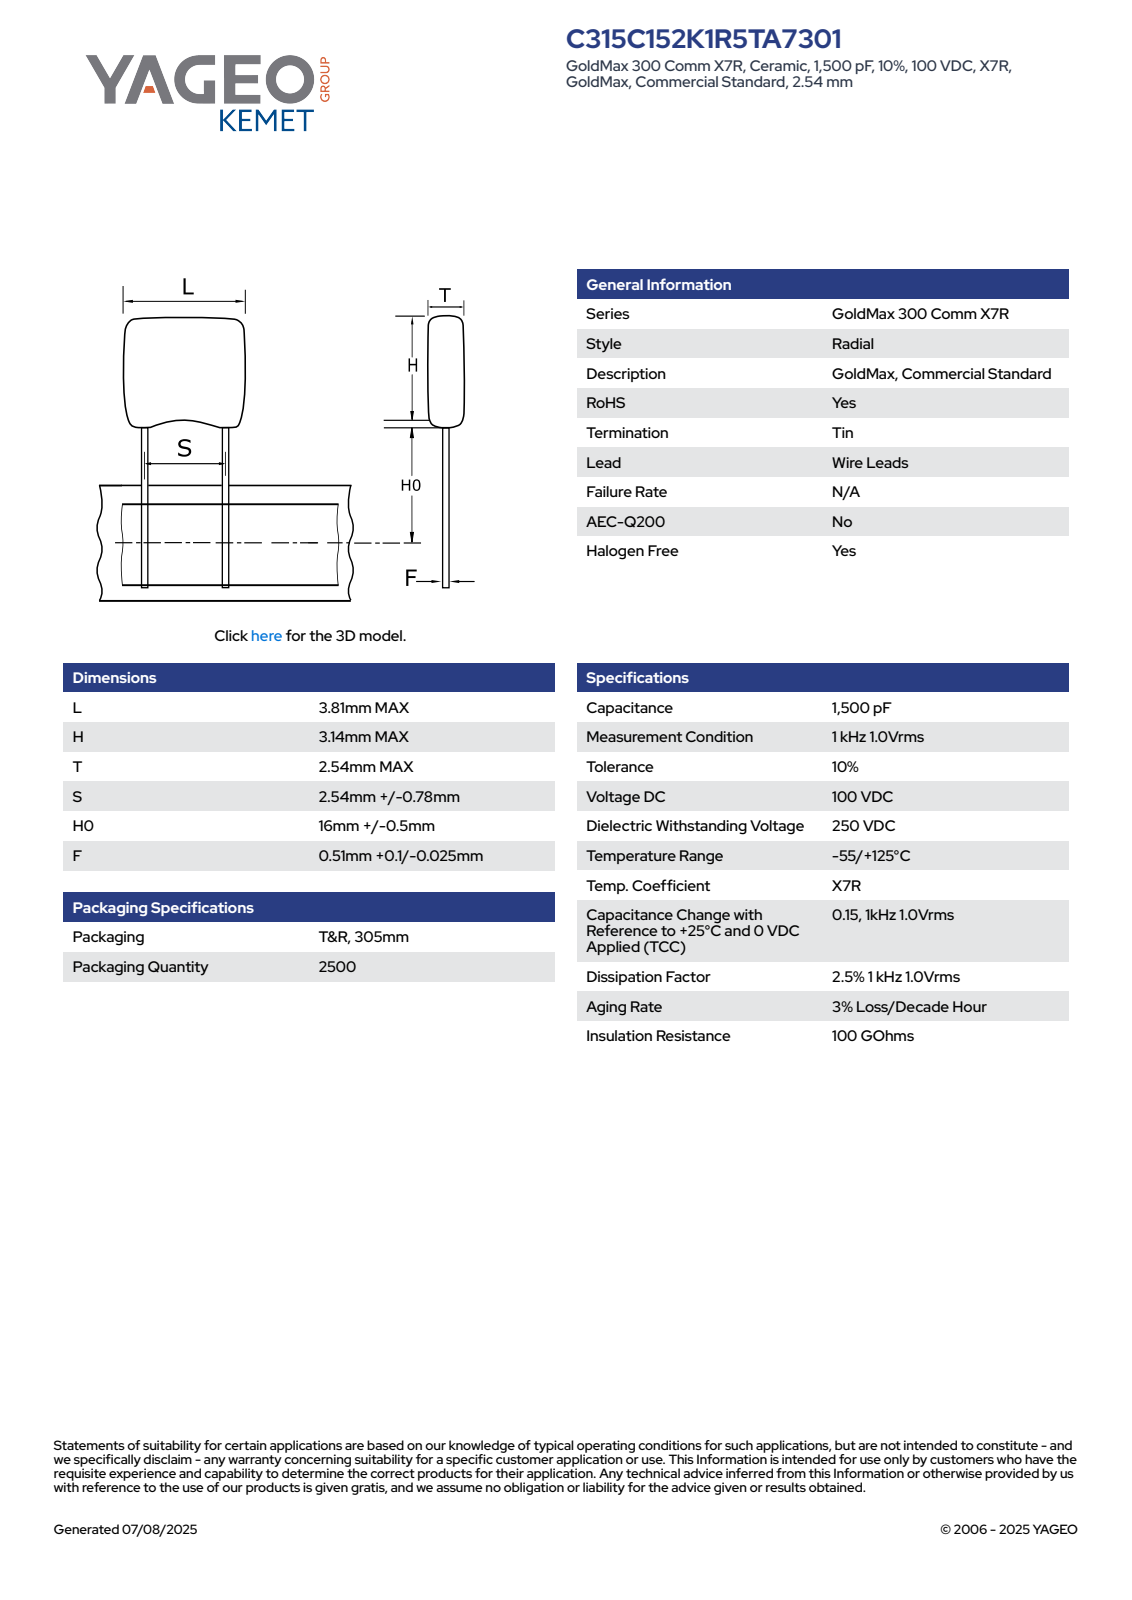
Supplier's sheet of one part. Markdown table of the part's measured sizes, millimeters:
| quantity | value |
| --- | --- |
| part name | CCR_KRCST_3.81X3.14_L3.81H3.14T2.54S2.54H016.5F0.61 |
| STEP written by | SolidWorks 2014 (AUTOMOTIVE_DESIGN) |
| units | millimeters |
| bodies | 4 solids, 83 faces (65 planar, 14 cylindrical, 4 other) |
| overall size | 20 × 3.81 × 2.54 |
| volume | 40 mm³ |
| surface area | 116 mm² |
| round bosses / shafts (diameter × count) | 0.61 × 2 |
| partial cylindrical surfaces (radius × count) | 0.75 × 10 |
| main face-to-face distances | 2.54, 3.81, 3.5, 16.5, 20, 0.41, 1.55, 18.46, 1.96, 1.54 |
